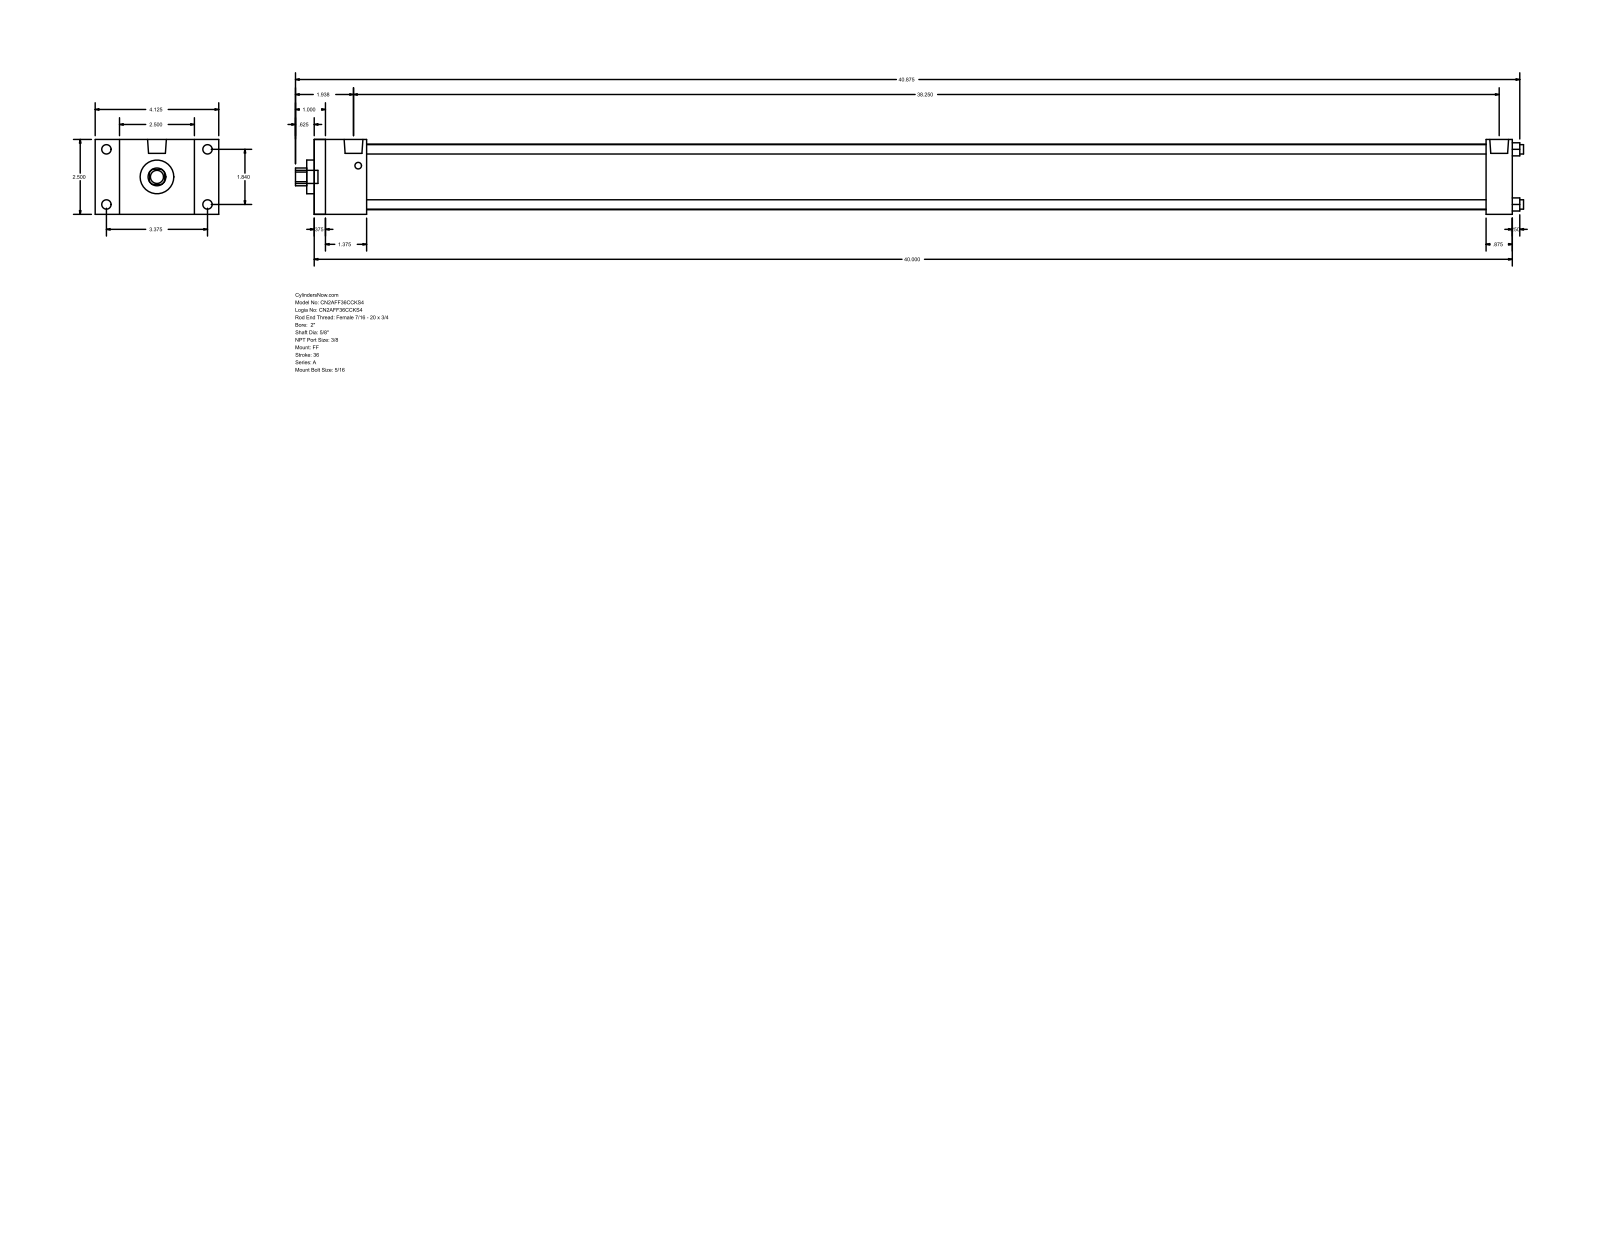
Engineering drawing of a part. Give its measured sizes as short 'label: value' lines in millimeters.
name: A_FF__0200_0.625
written by: GSSL Pune (CONFIG_CONTROL_DESIGN)
unit: mm
bodies: 0 solids, 92 faces (64 planar, 28 cylindrical, 0 other)
size: 1041.4 × 104.78 × 63.5
holes: 4× ⌀7.94, 1× ⌀15.88, 1× ⌀28.57, 1× ⌀55.63
bosses: 4× ⌀7.94, 4× ⌀5.56, 2× ⌀15.93, 1× ⌀11.11
rounds: 1× R7.54
face distances: 63.5, 1016, 9.52, 1006.48, 44.45, 993.77, 34.93, 984.25, 949.32, 971.55
hole spacings: 33.05, 46.74, 66.1
